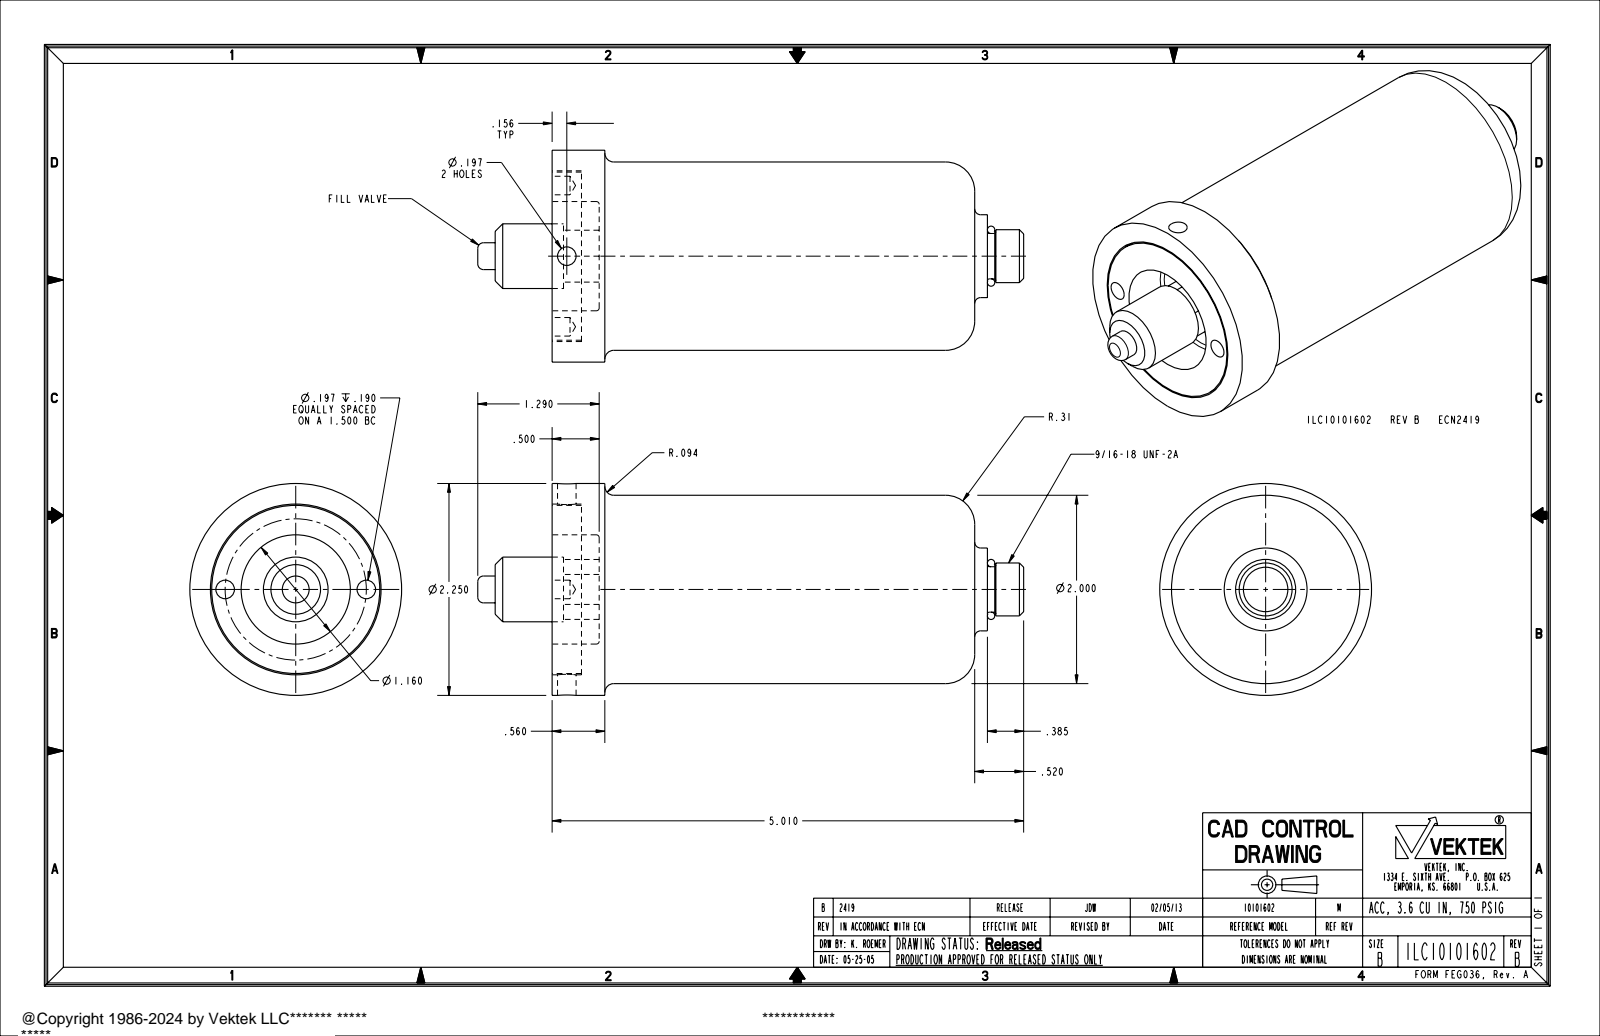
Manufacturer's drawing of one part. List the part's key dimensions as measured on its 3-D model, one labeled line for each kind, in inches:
Part name (STEP PRODUCT): ILC10101602
STEP written by: PRO/ENGINEER BY PARAMETRIC TECHNOLOGY CORPORATION, 2007460 (AUTOMOTIVE_DESIGN_CC2)
Units: inches
Bodies: 2 solids, 72 faces (18 planar, 28 cylindrical, 26 other)
Overall size (bounding box): 5.8 × 2.25 × 2.25
Volume: 14.44 in³ · Surface area: 45.15 in²
Round holes (diameter × count): ⌀0.197 ×3, ⌀1.16 ×1, ⌀1.813 ×1
Round bosses / shafts (diameter × count): ⌀2.25 ×1, ⌀2 ×1, ⌀1.785 ×1, ⌀0.88 ×1, ⌀0.687 ×1, ⌀0.562 ×1, ⌀0.482 ×1, ⌀0.285 ×1
Main face-to-face distances: 4.49, 3.99, 0.5, 0.135, 4.125, 4.625, 0.551, 4.065, 3.93, 0.06
Hole centre spacings: 0.75, 1.5
